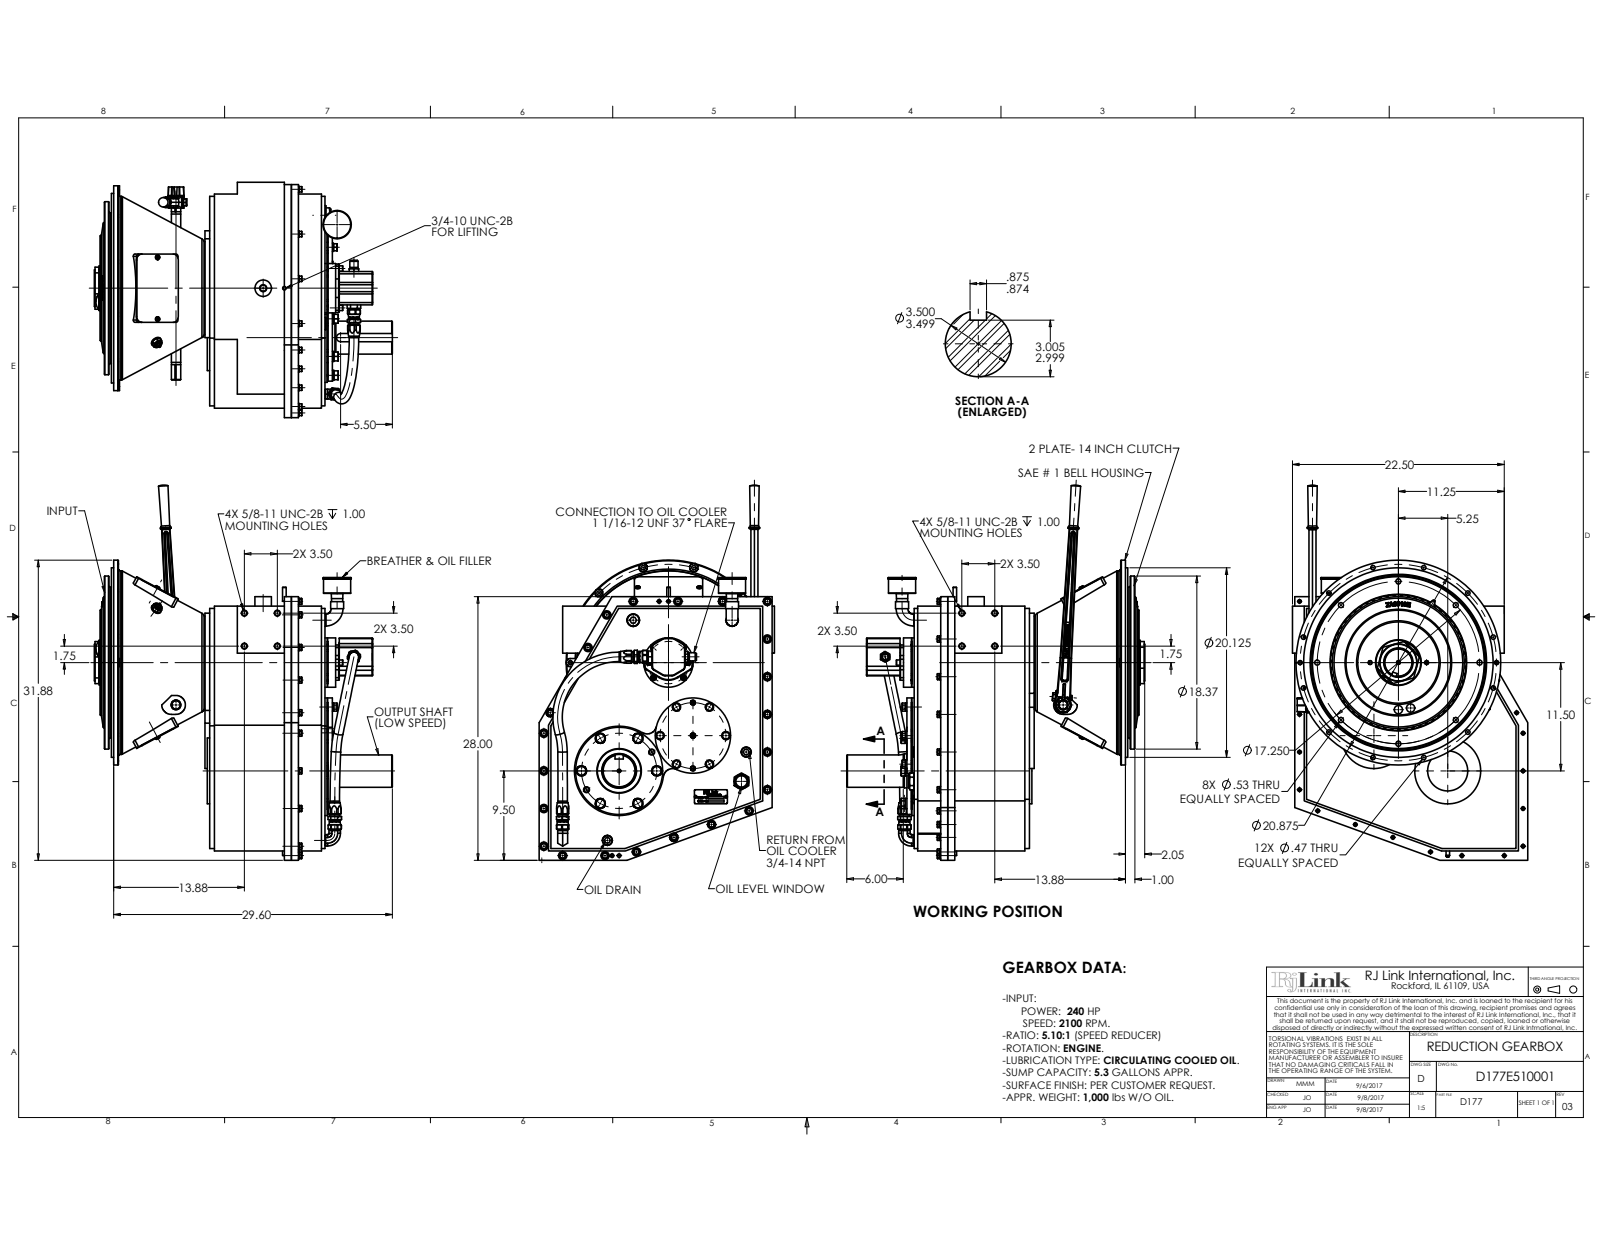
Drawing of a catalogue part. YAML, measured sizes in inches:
part_name: "SHK22405_2; HHCSZ_62-11X1_75; SHCS_38-16X1_00_18; D177009 (+8 more)"
step_written_by: "SolidWorks 2017 (AUTOMOTIVE_DESIGN)"
units: inches
bodies: {solids: 89, faces: 5534, planar: 2145, cylindrical: 2523, other: 866}
overall_size: [31.875, 31.595, 25]
volume: 86.67
surface_area: 8963
round_holes:
  - {diameter: 0.312, count: 39}
  - {diameter: 0.406, count: 33}
  - {diameter: 0.382, count: 29}
  - {diameter: 0.875, count: 26}
  - {diameter: 0.531, count: 24}
  - {diameter: 0.656, count: 13}
  - {diameter: 0.469, count: 12}
  - {diameter: 0.875, count: 11}
  - {diameter: 0.203, count: 9}
  - {diameter: 0.422, count: 8}
  - {diameter: 0.509, count: 6}
  - {diameter: 0.636, count: 6}
round_bosses_or_shafts:
  - {diameter: 0.375, count: 36}
  - {diameter: 0.683, count: 29}
  - {diameter: 0.561, count: 29}
  - {diameter: 0.625, count: 19}
  - {diameter: 0.25, count: 15}
  - {diameter: 0.375, count: 13}
  - {diameter: 0.5, count: 8}
  - {diameter: 1.079, count: 6}
partial_cylinders:
  - {radius: 0.25, count: 33}
  - {radius: 0.023, count: 32}
  - {radius: 0.037, count: 31}
  - {radius: 0.06, count: 14}
  - {radius: 0.5, count: 14}
  - {radius: 0.014, count: 12}
  - {radius: 0.19, count: 8}
  - {radius: 0.31, count: 8}
face_to_face_distances: [0.5, 12.25, 0.375, 11.875, 11.375, 11.75, 22.25, 1.5, 0.25, 1]
hole_center_spacings: [4.437, 6.787, 3.375, 4.013, 4, 7.686, 1.063, 7.813]
